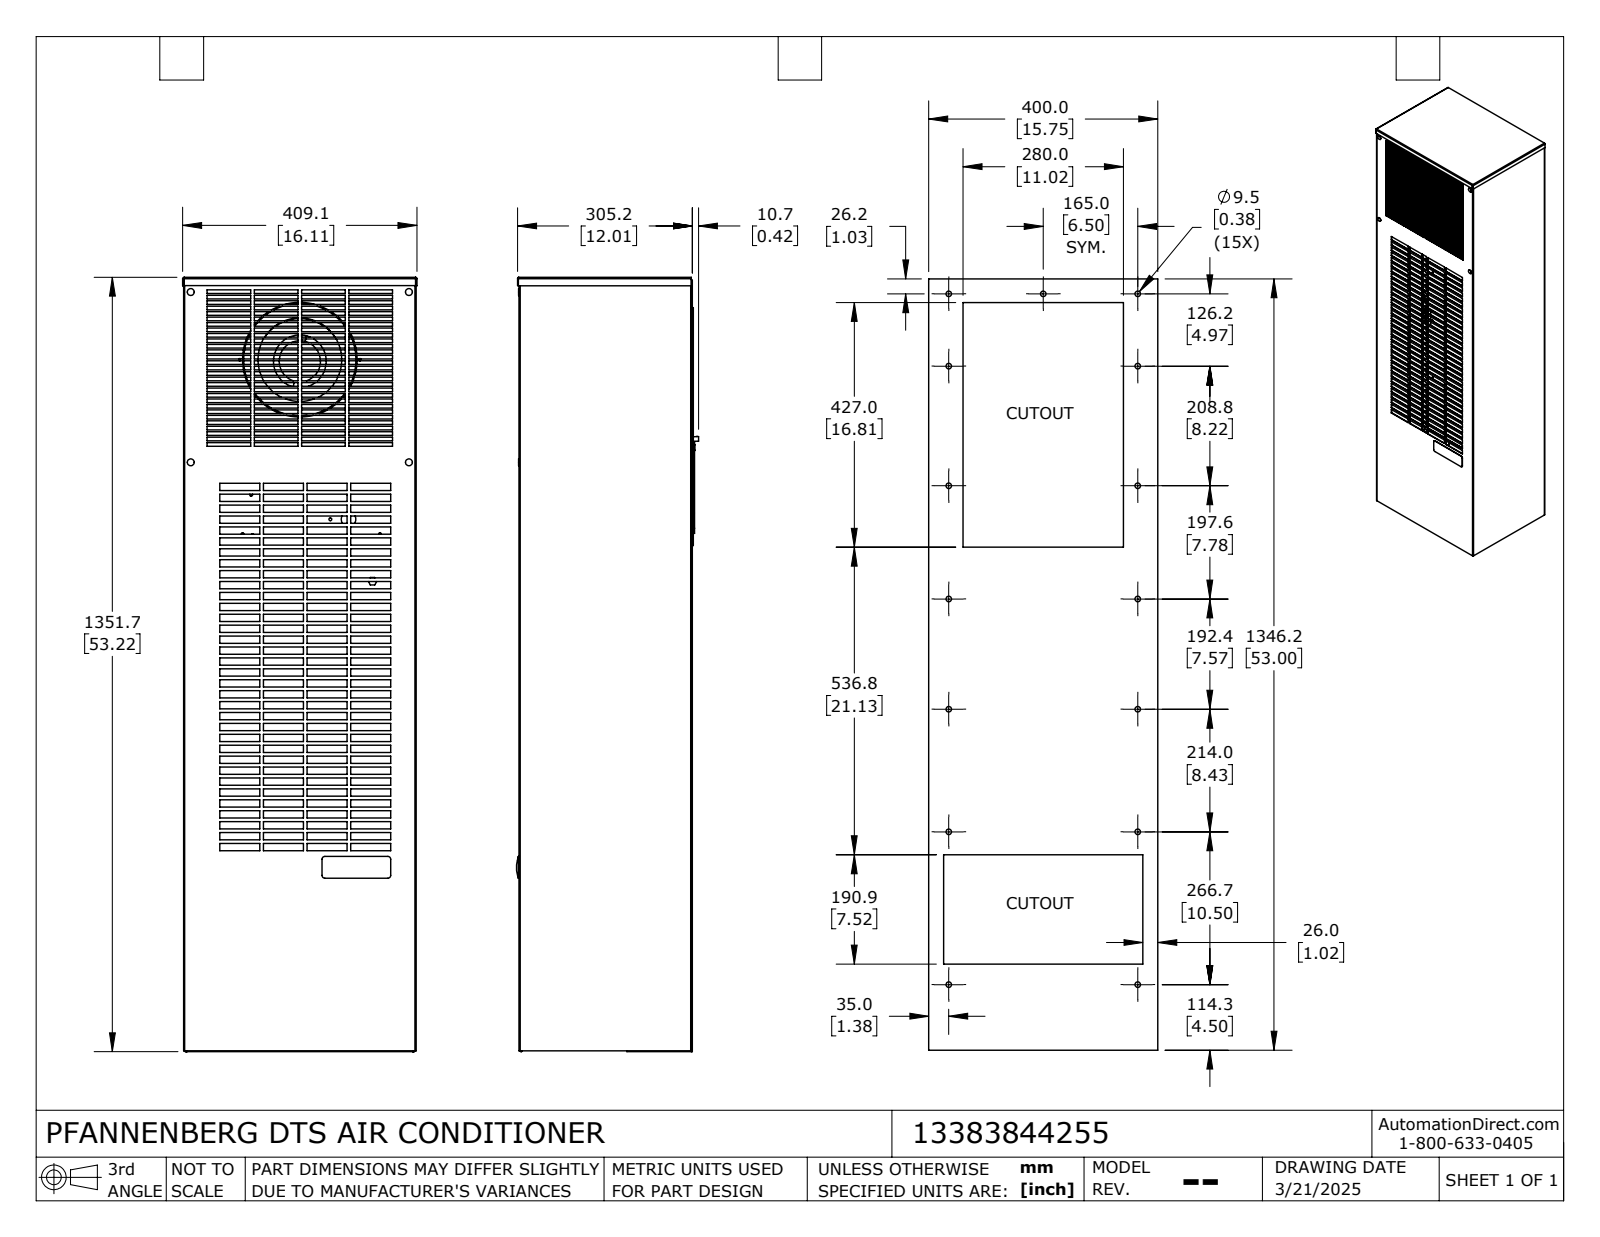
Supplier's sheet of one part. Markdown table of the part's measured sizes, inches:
| quantity | value |
| --- | --- |
| part name | 13383844255_Default |
| STEP written by | SolidWorks 2024 (CONFIG_CONTROL_DESIGN) |
| units | inches |
| bodies | 20 solids, 3087 faces (2071 planar, 908 cylindrical, 108 other) |
| overall size | 53.217 × 16.106 × 12.518 |
| volume | 433.9 in³ |
| surface area | 10 861 in² |
| round holes (diameter × count) | 0.165 × 64, 0.165 × 18, 0.157 × 15, 0.375 × 15, 0.165 × 10, 0.197 × 8, 0.25 × 8, 0.236 × 7, 0.13 × 5, 0.177 × 4, 0.217 × 4, 0.022 × 2 |
| round bosses / shafts (diameter × count) | 0.079 × 5, 0.472 × 4, 0.276 × 2, 0.031 × 2, 8.858 × 1, 8.78 × 1, 5.866 × 1, 3.622 × 1 |
| partial cylindrical surfaces (radius × count) | 0.125 × 140, 0.031 × 23, 0.079 × 19, 0.031 × 8, 0.079 × 8, 0.197 × 8, 0.05 × 7, 0.118 × 5 |
| main face-to-face distances | 0.048, 0.048, 15.941, 0.166, 15.99, 15.893, 4.362, 4.528, 11.923, 7.561 |
| hole center spacings | 0.02, 12.992, 4, 8, 8.75, 16, 20.611, 0.02 |
